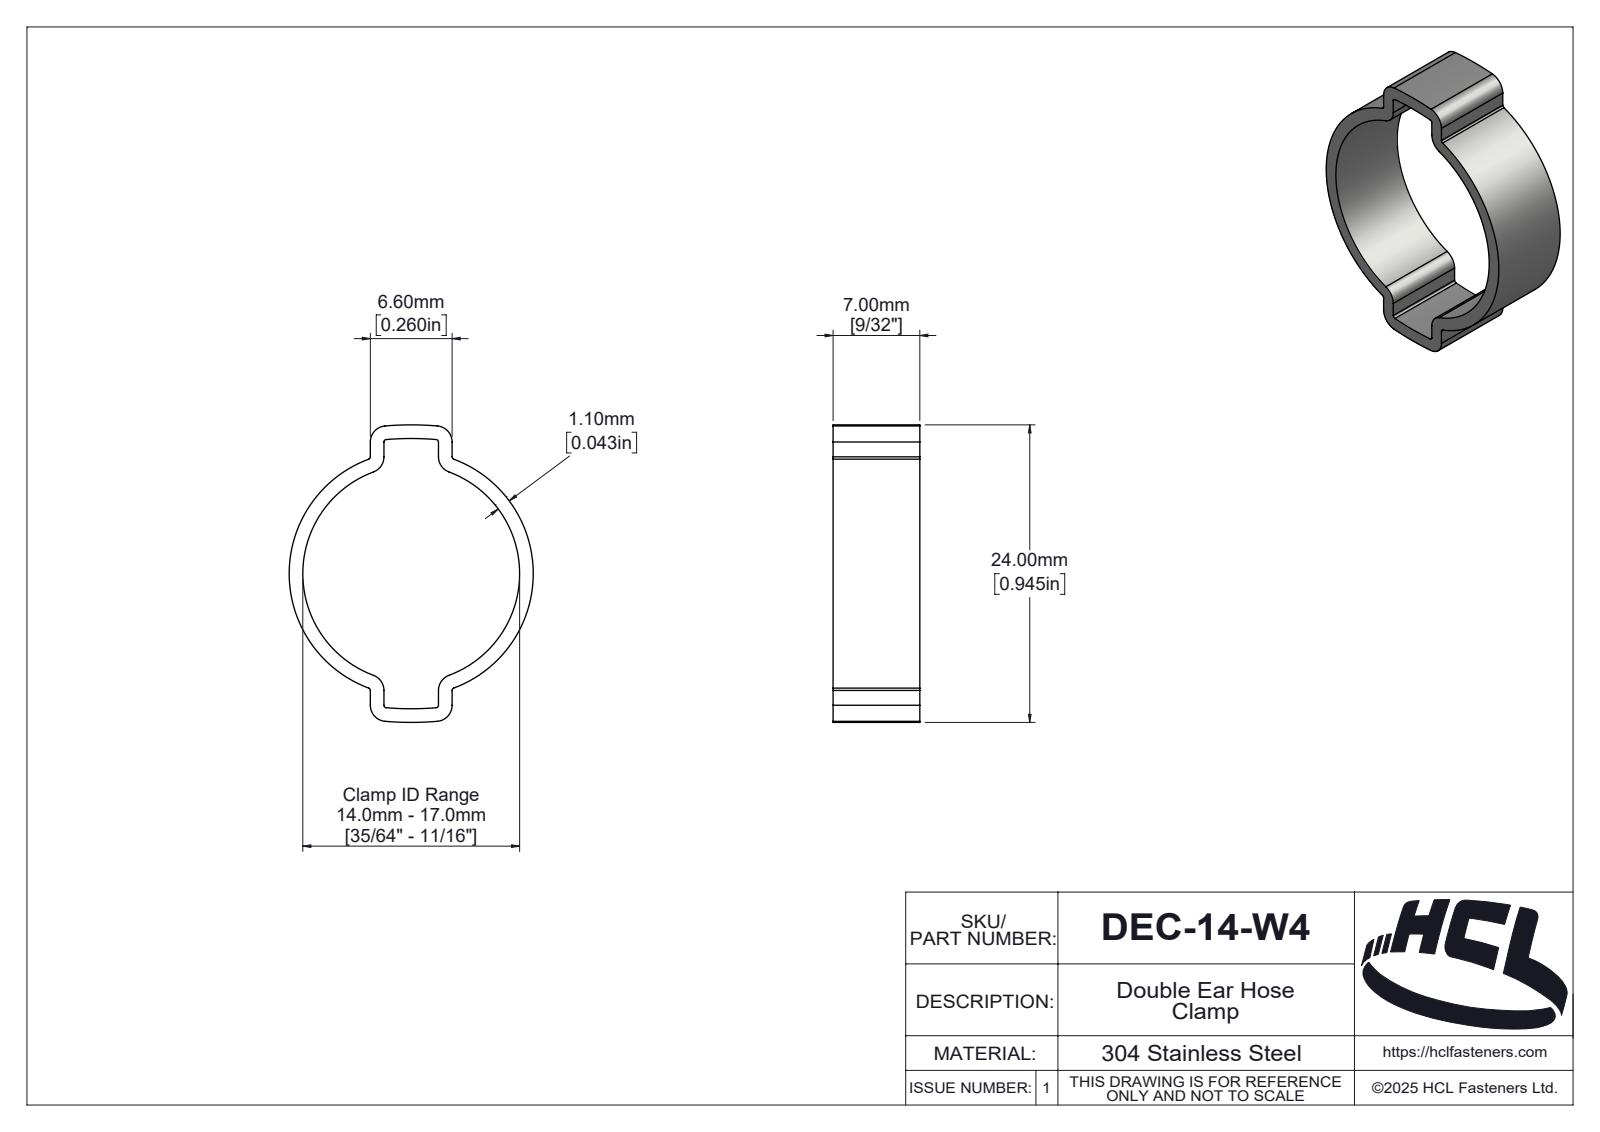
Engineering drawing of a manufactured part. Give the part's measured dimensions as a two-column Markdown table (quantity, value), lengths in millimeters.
| quantity | value |
| --- | --- |
| part name | DEC-14-W4 |
| STEP written by | SolidWorks 2025 (AUTOMOTIVE_DESIGN) |
| units | millimeters |
| bodies | 1 solid, 137 faces (12 planar, 67 cylindrical, 58 other) |
| overall size | 24 × 19.7 × 7 |
| volume | 510 mm³ |
| surface area | 1 078 mm² |
| partial cylindrical surfaces (radius × count) | 0.2 × 8, 1.3 × 8, 24.25 × 2, 25.35 × 2, 0.2 × 1, 0.81 × 1, 1.01 × 1, 1.06 × 1 |
| main face-to-face distances | 7, 1.1, 5.5, 6.6, 4.4, 3.18, 2.08, 2.32, 3.42, 3.03 |
